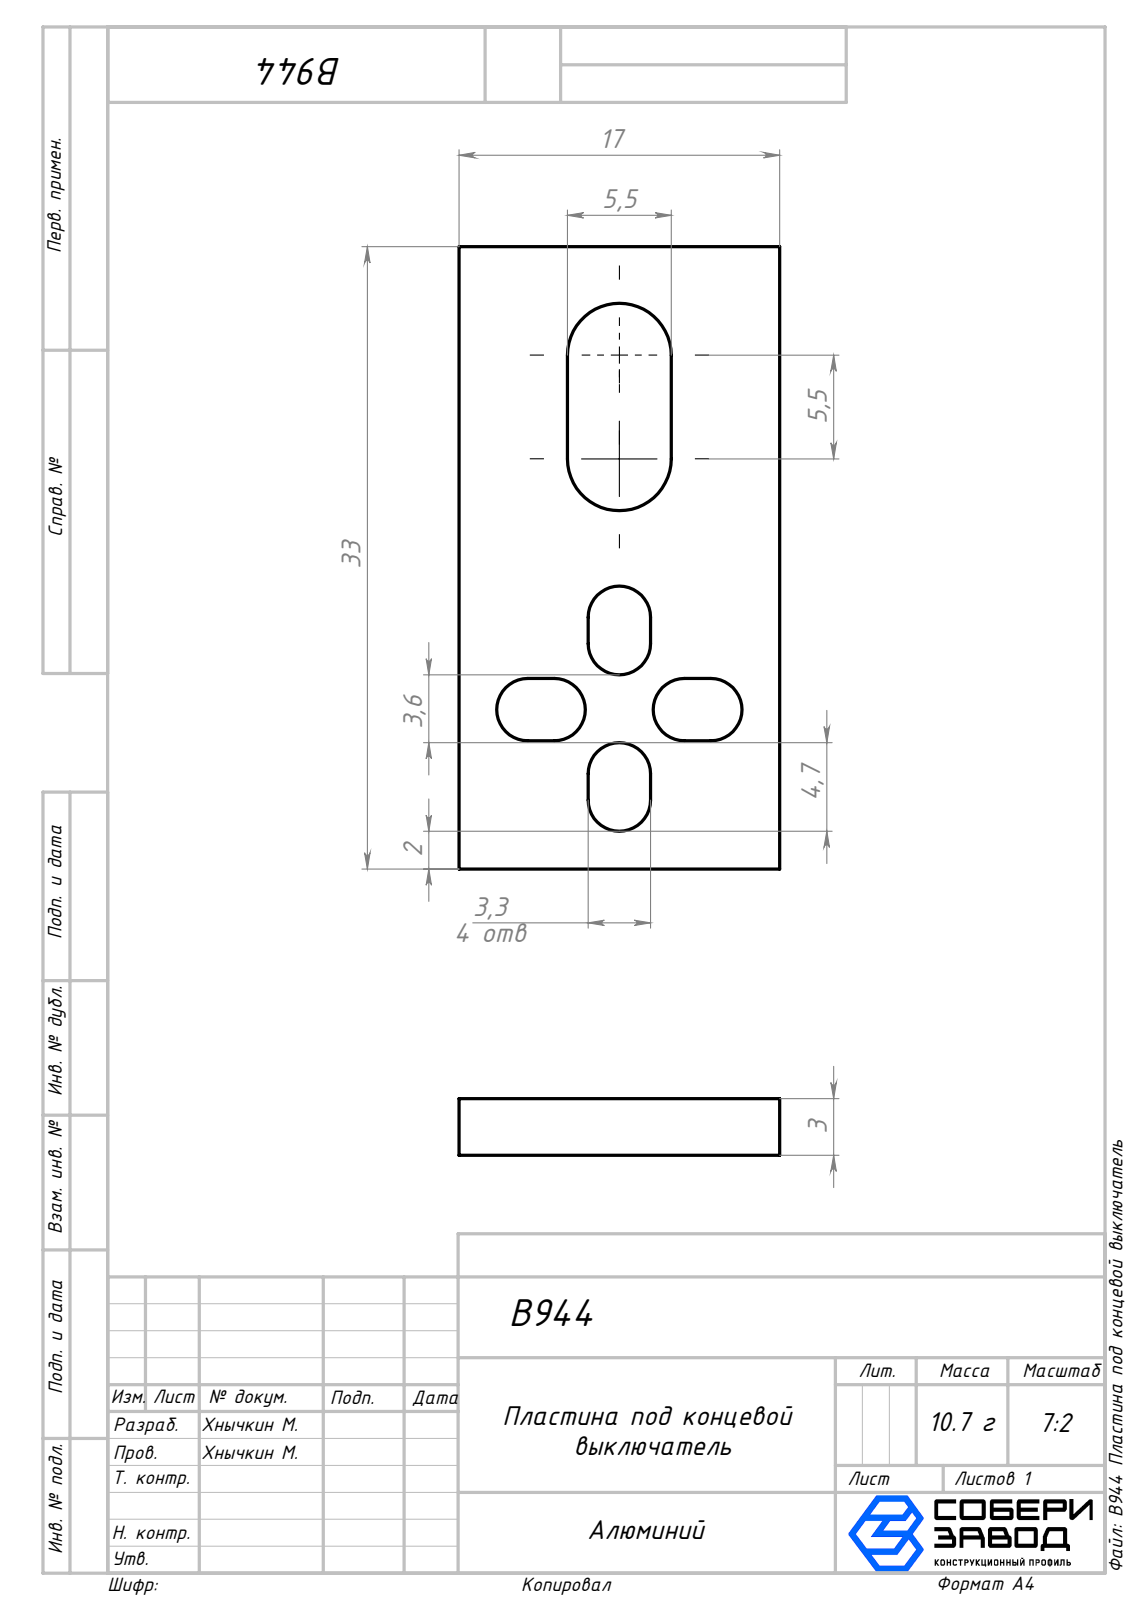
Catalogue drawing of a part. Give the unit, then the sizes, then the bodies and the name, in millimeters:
Units: millimetres
Overall size (bounding box): 33 × 17 × 3
Partial cylindrical surfaces — rounded edges, fillets, slot ends (radius × count): R1.65 ×8, R2.75 ×2
Main face-to-face distances: 3, 17, 33, 5.75, 11.25, 3.3, 6.85, 10.15, 1.1, 4.4
Volume: 1 363 mm³ · Surface area: 1 451 mm²
Bodies: 1 solid, 29 faces (16 planar, 13 cylindrical, 0 other)
Part name (STEP PRODUCT): B944 Пластина под концевой выключатель
STEP written by: SolidWorks 2026 (AUTOMOTIVE_DESIGN)
